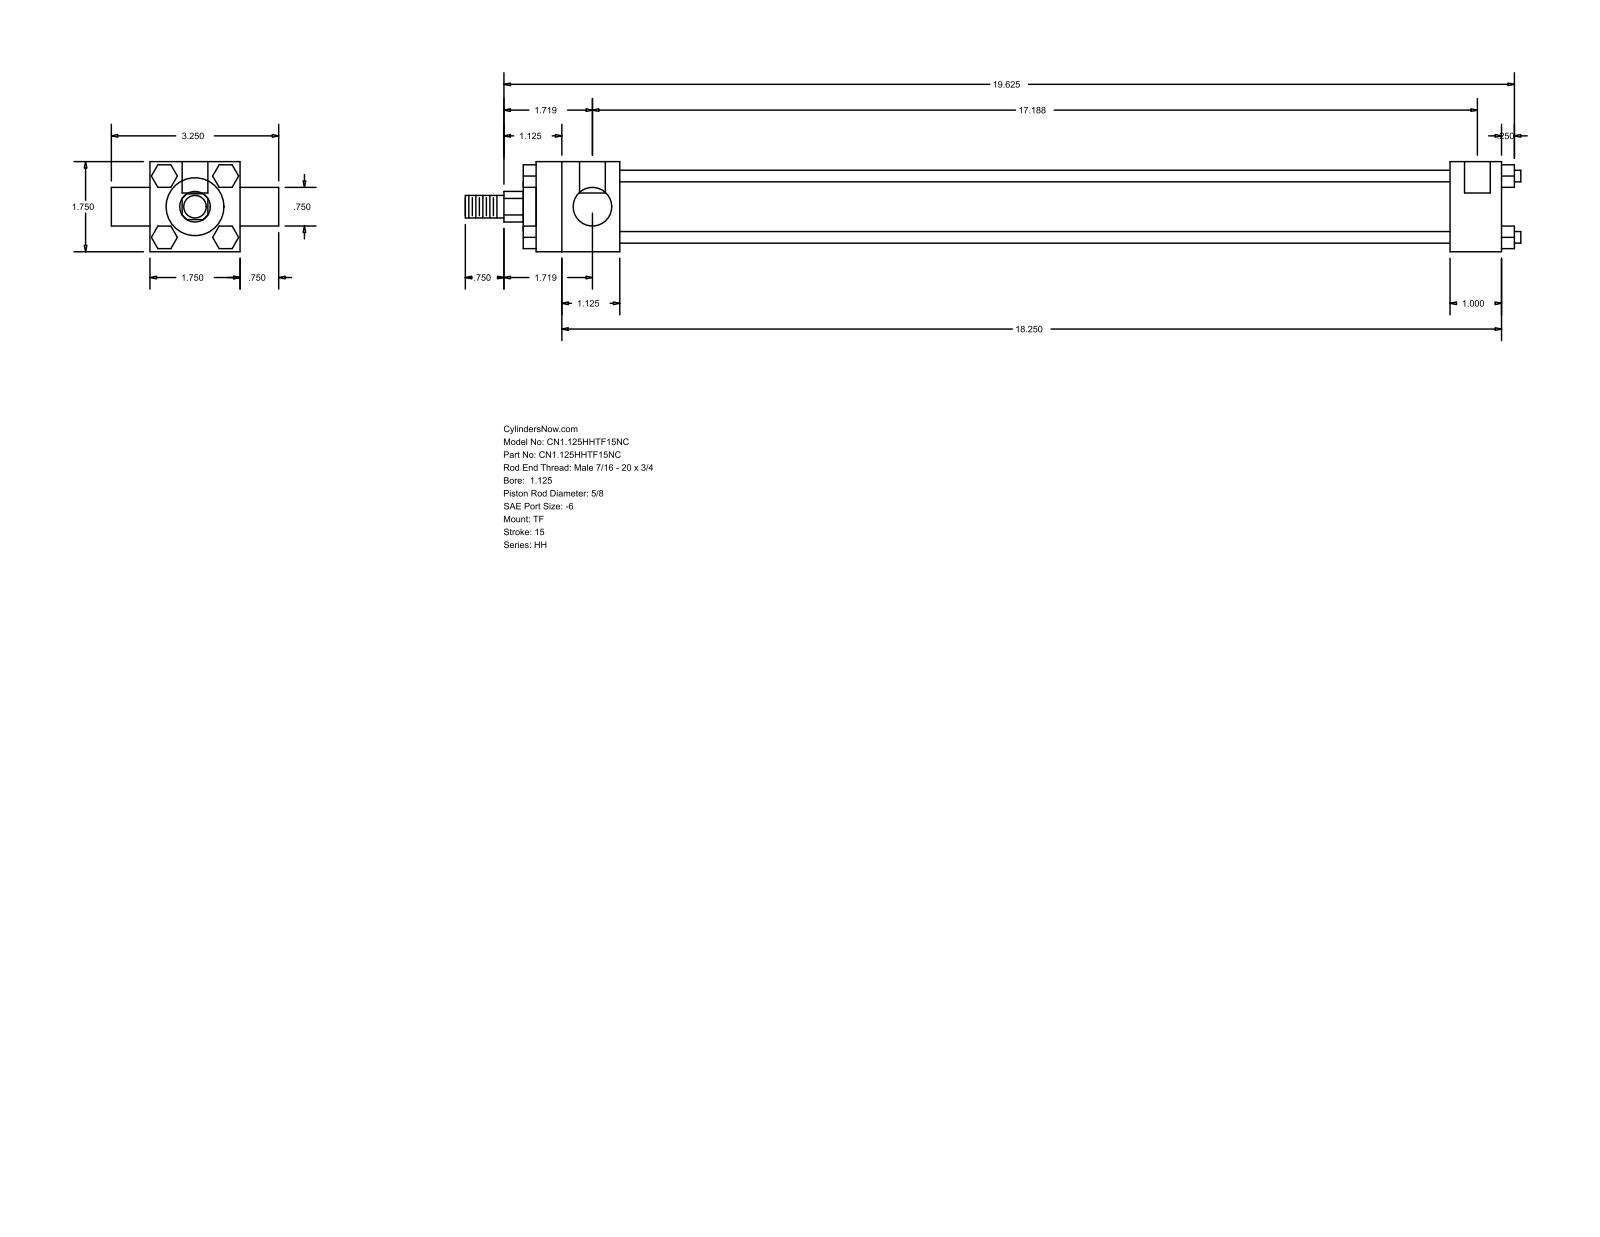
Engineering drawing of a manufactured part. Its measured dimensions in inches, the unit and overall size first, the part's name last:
Units: inches
Overall size (bounding box): 20.5 × 3.25 × 1.75
Round holes (diameter × count): ⌀0.219 ×3, ⌀0.5 ×2
Round bosses / shafts (diameter × count): ⌀0.225 ×4, ⌀1.375 ×1, ⌀1.125 ×1, ⌀0.75 ×1, ⌀0.625 ×1, ⌀0.437 ×1
Partial cylindrical surfaces — rounded edges, fillets, slot ends (radius × count): R0.297 ×1
Main face-to-face distances: 1.75, 0.437, 16.125, 17.125, 1, 1.625, 17.75, 18.75, 1.875, 0.25
Hole centre spacings: 0.125, 17.063, 17.187
Bodies: 0 solids, 120 faces (92 planar, 28 cylindrical, 0 other)
Part name (STEP PRODUCT): HH_TF__0112_0.625
STEP written by: GSSL Pune (CONFIG_CONTROL_DESIGN)
